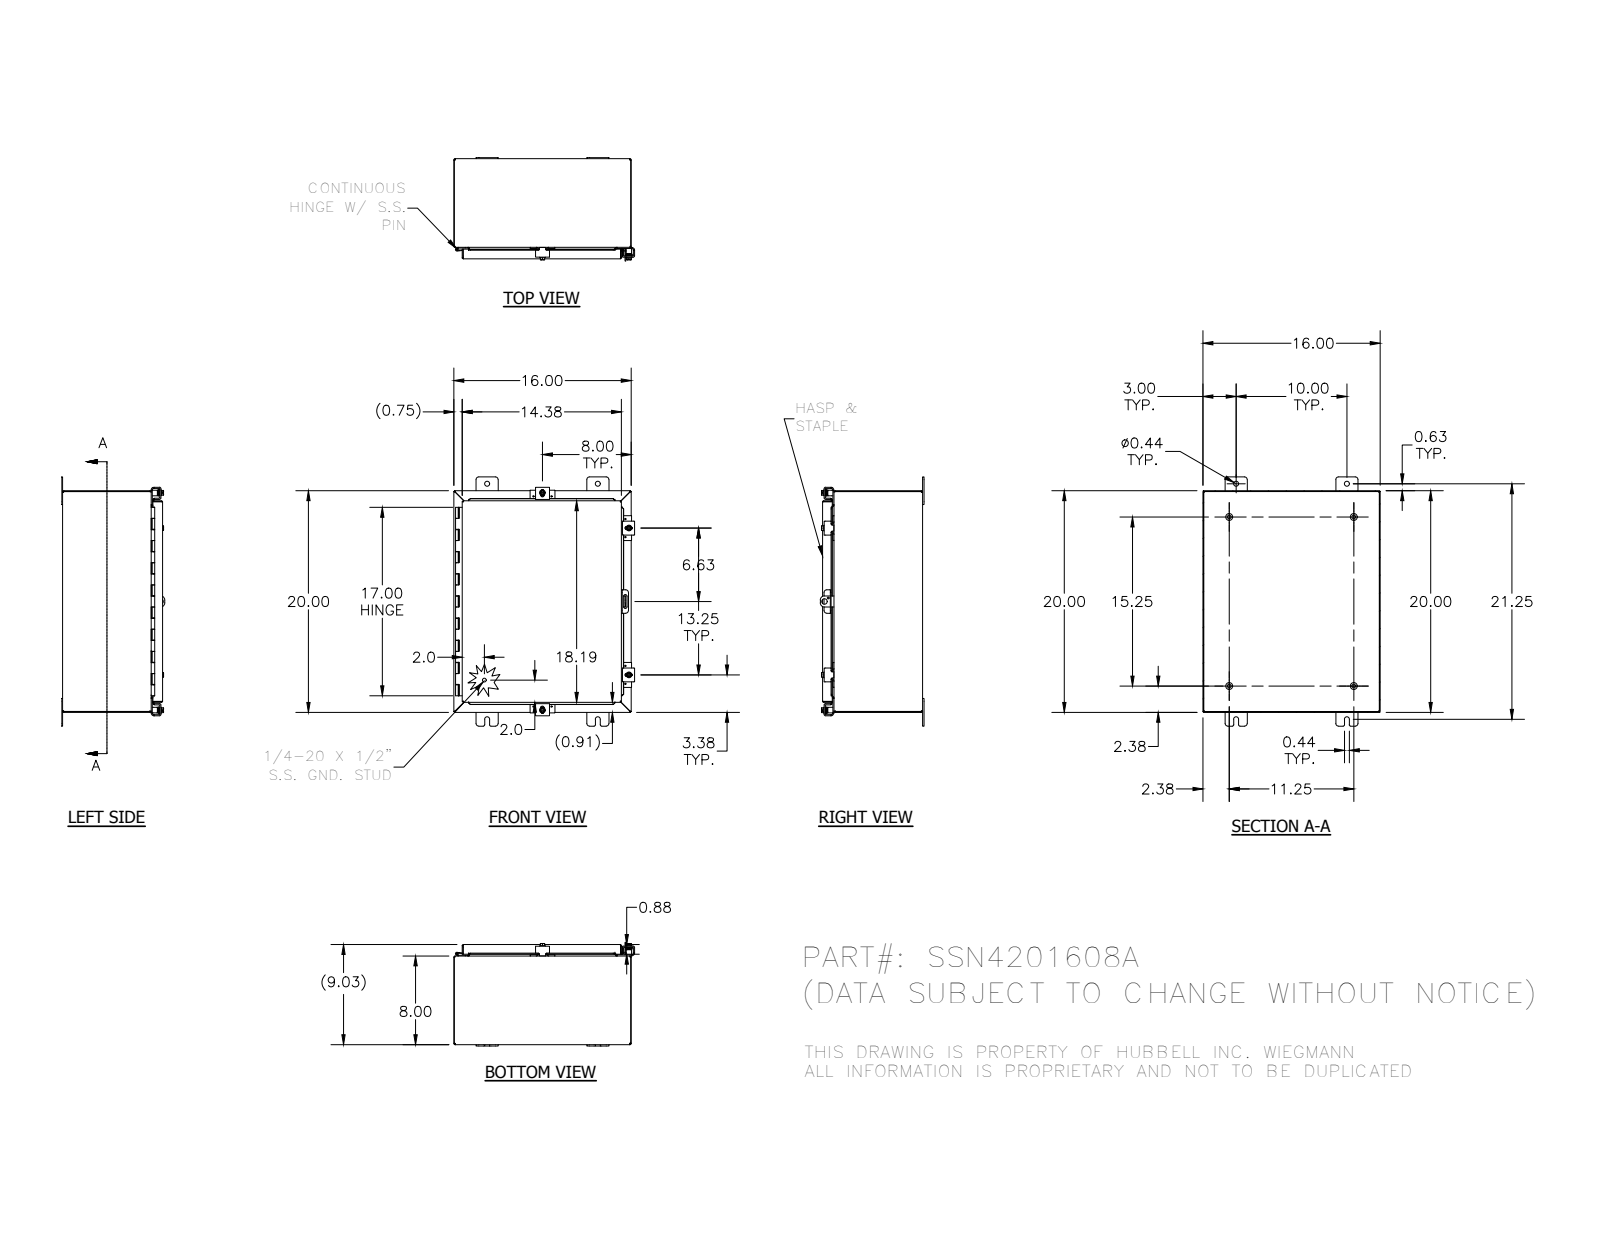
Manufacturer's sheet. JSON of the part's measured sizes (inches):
{"part_name": "32874-20L; 30824; 38412; 30818 (+8 more)", "step_written_by": "SolidWorks 2014 (AUTOMOTIVE_DESIGN)", "units": "inches", "bodies": {"solids": 37, "faces": 1428, "planar": 575, "cylindrical": 612, "other": 241}, "overall_size": [22.5, 16.216, 9.355], "volume_in3": 114.3, "surface_area_in2": 2988, "round_holes": [[0.11, 8], [0.211, 4], [0.281, 4], [0.3, 4], [0.438, 4], [0.125, 1], [0.156, 1], [0.5, 1]], "round_bosses_or_shafts": [[0.25, 6], [0.625, 4], [0.52, 4], [0.5, 4], [0.35, 4], [0.33, 4], [0.337, 1], [0.12, 1]], "partial_cylinders_radius": [[0.03, 49], [0.125, 33], [0.25, 29], [0.031, 23], [0.105, 23], [0.062, 14], [0.07, 8], [0.141, 8]], "face_to_face_distances": [0.074, 8.959, 15.926, 8.885, 9.033, 19.926, 7.926, 1.033, 15.852, 16], "hole_center_spacings": [0.876, 19.306, 13.25, 0.876, 1.625, 1.625, 4.189, 4.341]}
